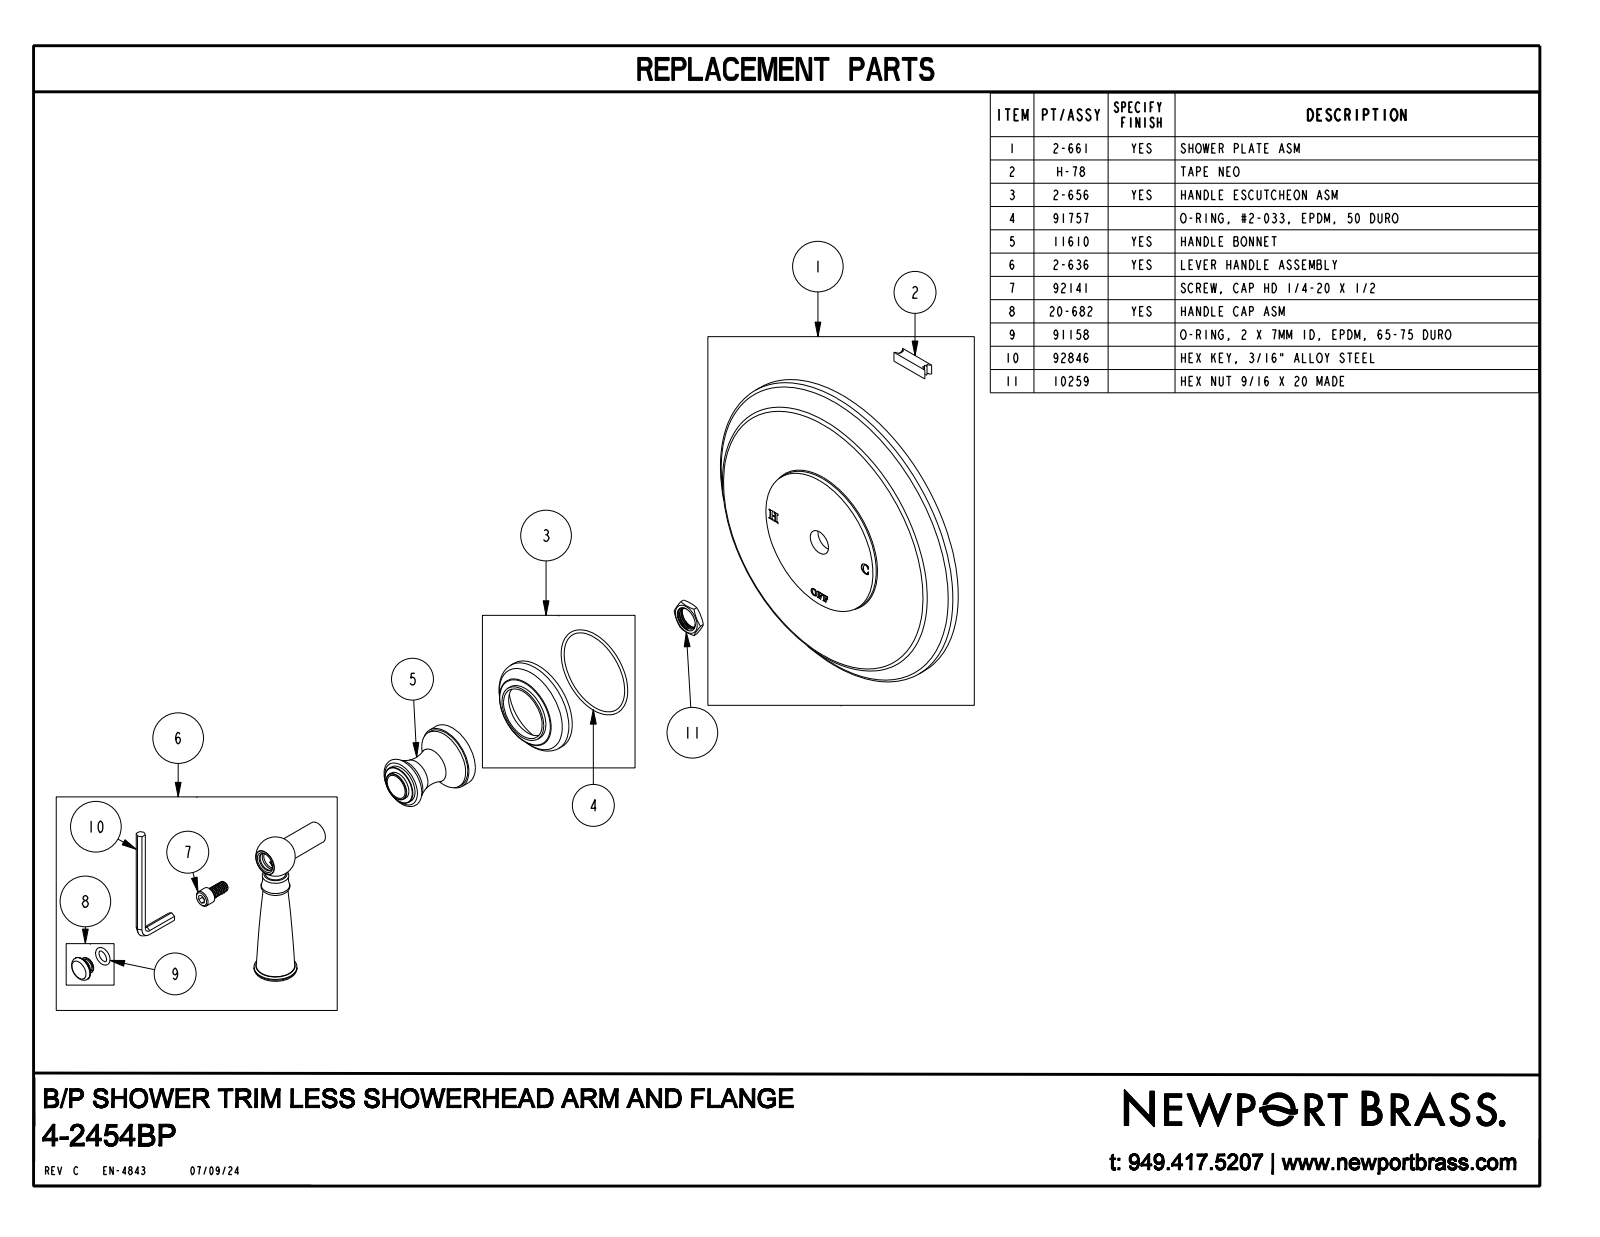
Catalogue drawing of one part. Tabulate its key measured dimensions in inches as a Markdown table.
| quantity | value |
| --- | --- |
| part name | 4-2454BP |
| STEP written by | CREO PARAMETRIC BY PTC INC, 2018400 (CONFIG_CONTROL_DESIGN) |
| units | inches |
| bodies | 1 solid, 213 faces (42 planar, 20 cylindrical, 151 other) |
| overall size | 7.5 × 7.5 × 4.072 |
| volume | 30.3 in³ |
| surface area | 115.7 in² |
| round bosses / shafts (diameter × count) | 7.5 × 1, 2.2 × 1, 1.49 × 1, 1.42 × 1, 0.983 × 1, 0.9 × 1, 0.66 × 1, 0.56 × 1 |
| main face-to-face distances | 0.625, 0.75, 0.125, 1.18, 0.555, 0.43, 0.08, 2.92, 2.295, 2.17 |
